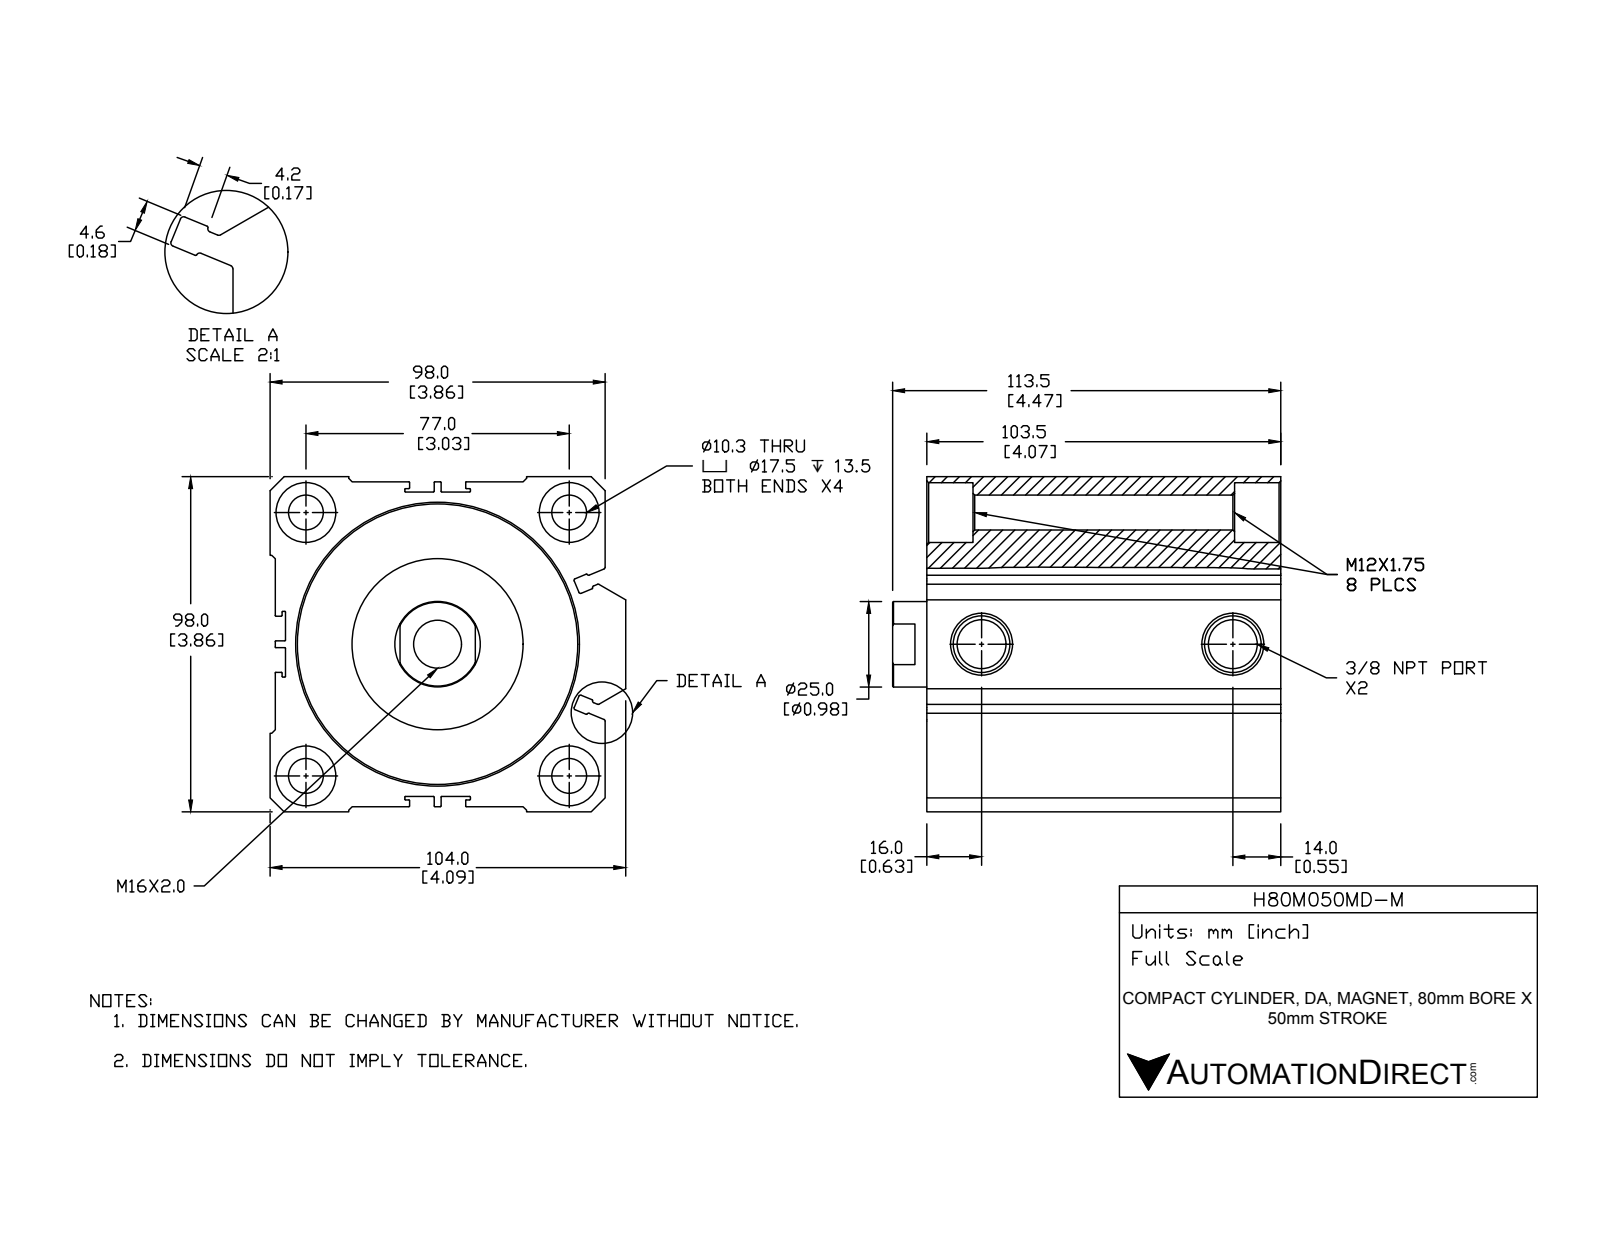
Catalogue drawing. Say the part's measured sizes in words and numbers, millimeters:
The part is named "H80M050MD-M; H80M050MD-M-BODY; H80M050MD-M-PISTON". Its 3-D file was written by "SolidWorks 2015 (CONFIG_CONTROL_DESIGN)". It is 2 solids with 261 faces: 105 planar, 103 cylindrical and 53 other. Overall it measures 113.5 by 104 by 98 millimeters. Its volume is 648 697 cubic millimeters and its surface area 140 946 square millimeters. Round holes: 4 of diameter 10.2, 4 of diameter 17.5, 2 of diameter 14.27, 1 of diameter 14, 1 of diameter 25, 1 of diameter 45.51, 1 of diameter 80, 1 of diameter 82. Round bosses or shafts: 1 of diameter 50, 1 of diameter 39. Partial cylindrical surfaces (rounded edges, fillets, slot ends): 40 of radius 0.2, 12 of radius 0.5. The main face-to-face distances are 1.5, 96.5, 98, 50, 93.5, 4.5, 3, 9, 36.1, 27.1. The hole center spacings are 54.45, 77, 108.89, 73.5.
